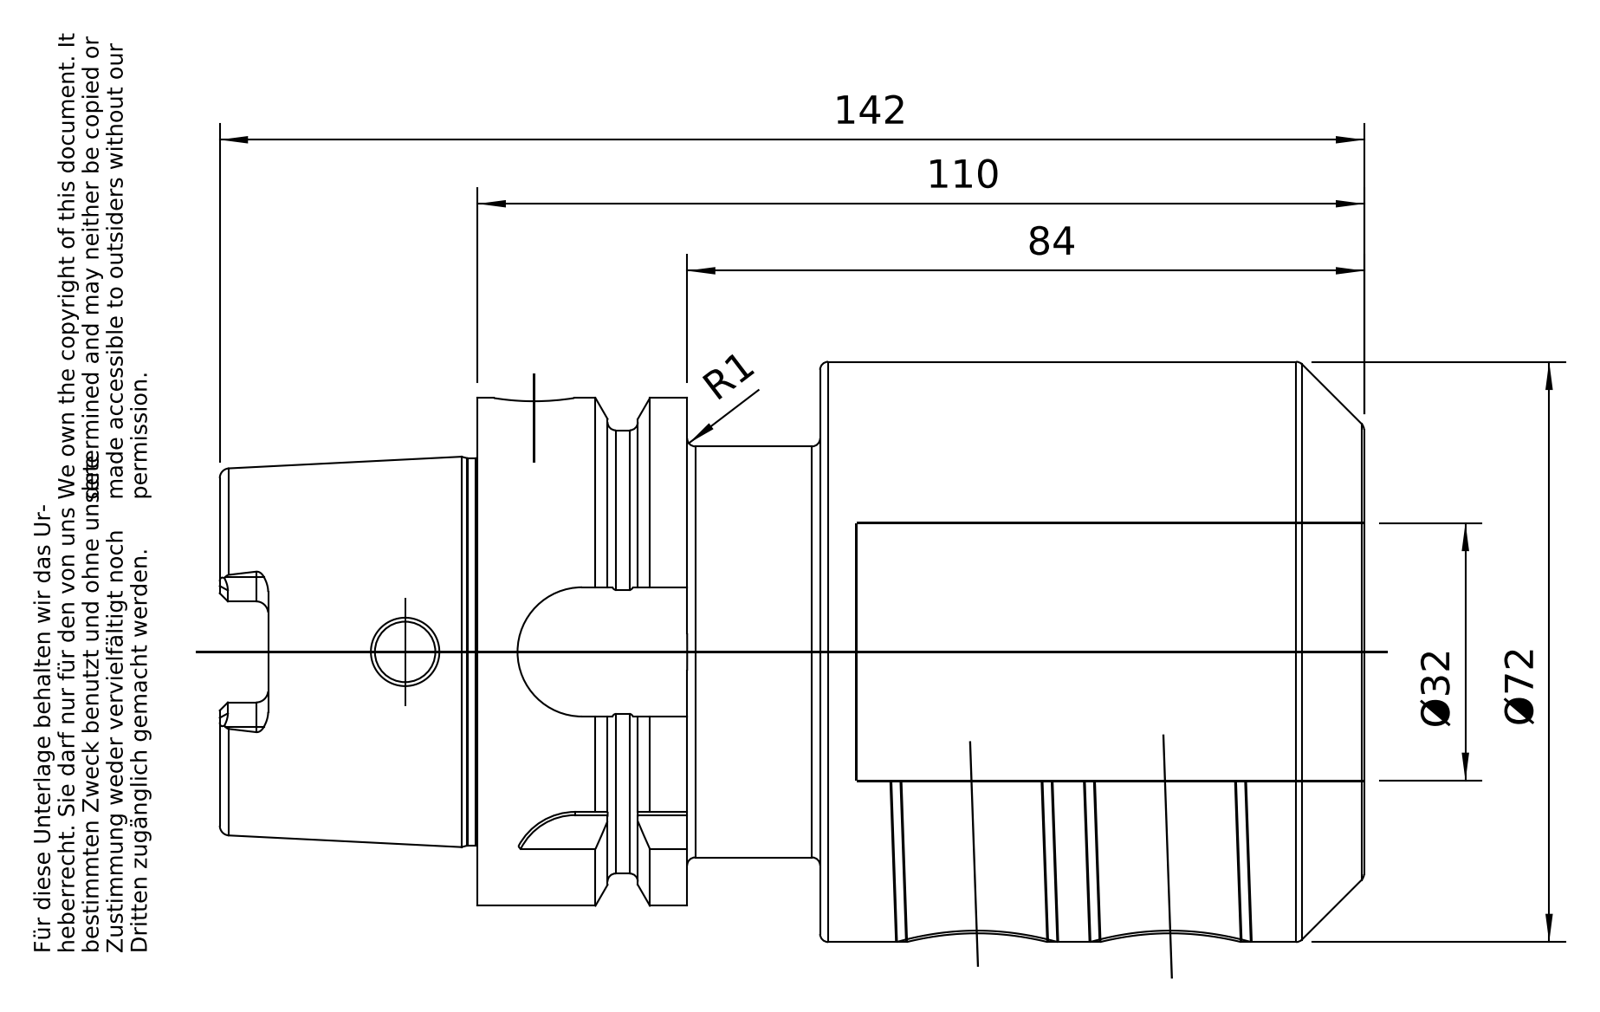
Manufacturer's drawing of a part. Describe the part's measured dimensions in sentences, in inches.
The part is named "A63-030-32". Its 3-D file was written by "PRO/ENGINEER BY PARAMETRIC TECHNOLOGY CORPORATION, 2010430 (CONFIG_CONTROL_DESIGN)". It is 1 solid with 193 faces: 60 planar, 58 cylindrical and 75 other. Overall it measures 5.591 by 2.835 by 2.835 inches. Its volume is 20.01 cubic inches and its surface area 82.29 square inches. Round holes: 2 of diameter 0.689, 2 of diameter 0.787, 1 of diameter 0.295, 1 of diameter 0.394, 1 of diameter 0.666, 1 of diameter 0.721, 1 of diameter 0.735, 1 of diameter 1.26, 1 of diameter 1.339, 1 of diameter 1.575. Round bosses or shafts: 1 of diameter 2.835, 1 of diameter 2.48, 1 of diameter 2.165, 1 of diameter 2.008, 1 of diameter 1.891, 1 of diameter 0.709. Partial cylindrical surfaces (rounded edges, fillets, slot ends): 6 of radius 0.059, 4 of radius 0.118, 1 of radius 0.315, 1 of radius 0.316, 1 of radius 0.355. The main face-to-face distances are 2.657, 1.673, 4.331, 1.024, 0.65, 3.307, 2.087, 1.063, 0.413, 2.244. The hole center spacings are 0.945.
